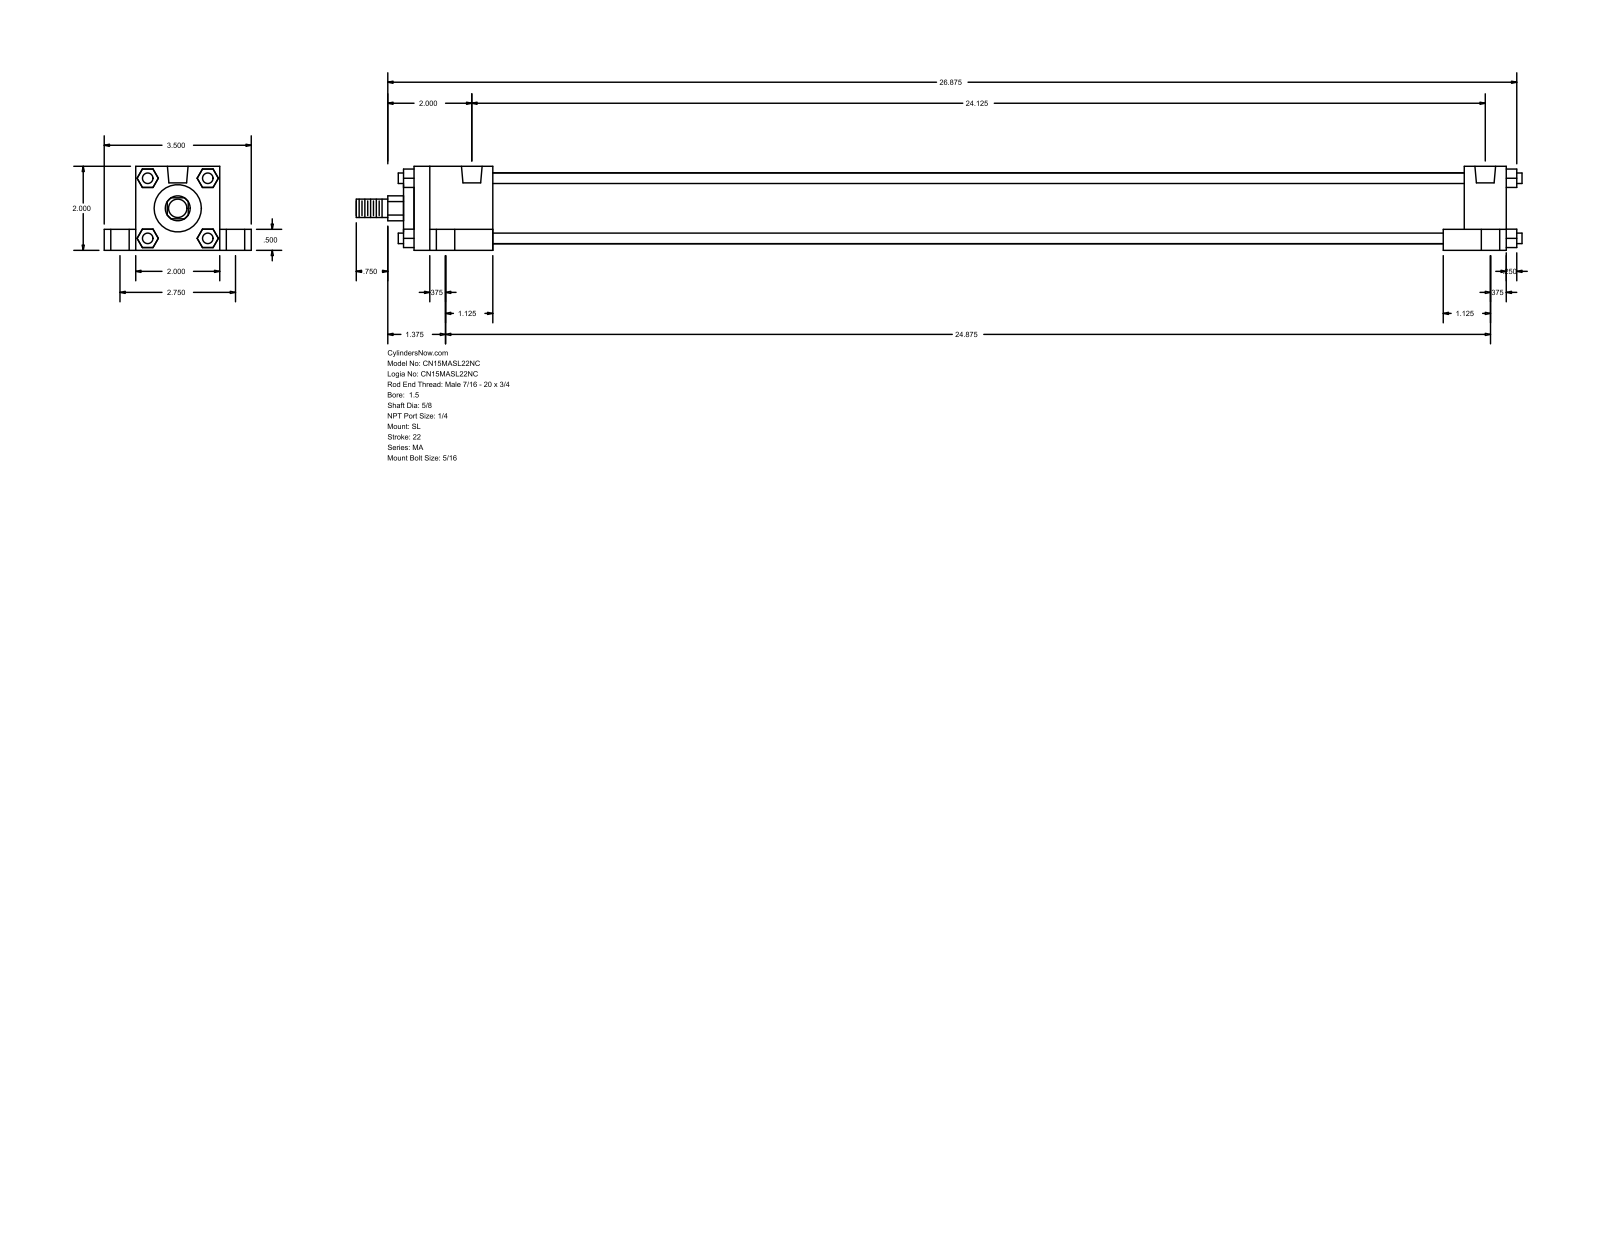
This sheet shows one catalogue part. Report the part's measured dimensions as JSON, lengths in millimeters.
{"part_name": "MA_SL__0150_0.625", "step_written_by": "GSSL Pune (CONFIG_CONTROL_DESIGN)", "units": "millimeters", "bodies": {"solids": 0, "faces": 148, "planar": 112, "cylindrical": 36, "other": 0}, "overall_size": [704.85, 88.9, 50.8], "round_holes": [[7.94, 4], [11.11, 4], [17.46, 4], [12.49, 2]], "round_bosses_or_shafts": [[6.35, 4], [42.93, 1], [28.57, 1], [15.88, 1], [11.11, 1]], "partial_cylinders_radius": [[7.54, 1]], "face_to_face_distances": [50.8, 19.05, 38.1, 69.85, 12.7, 660.39, 6.35, 9.52, 666.74, 635], "hole_center_spacings": [35.06, 38.36, 69.84, 612.78, 616.94, 629.63, 631.83, 635.68]}
